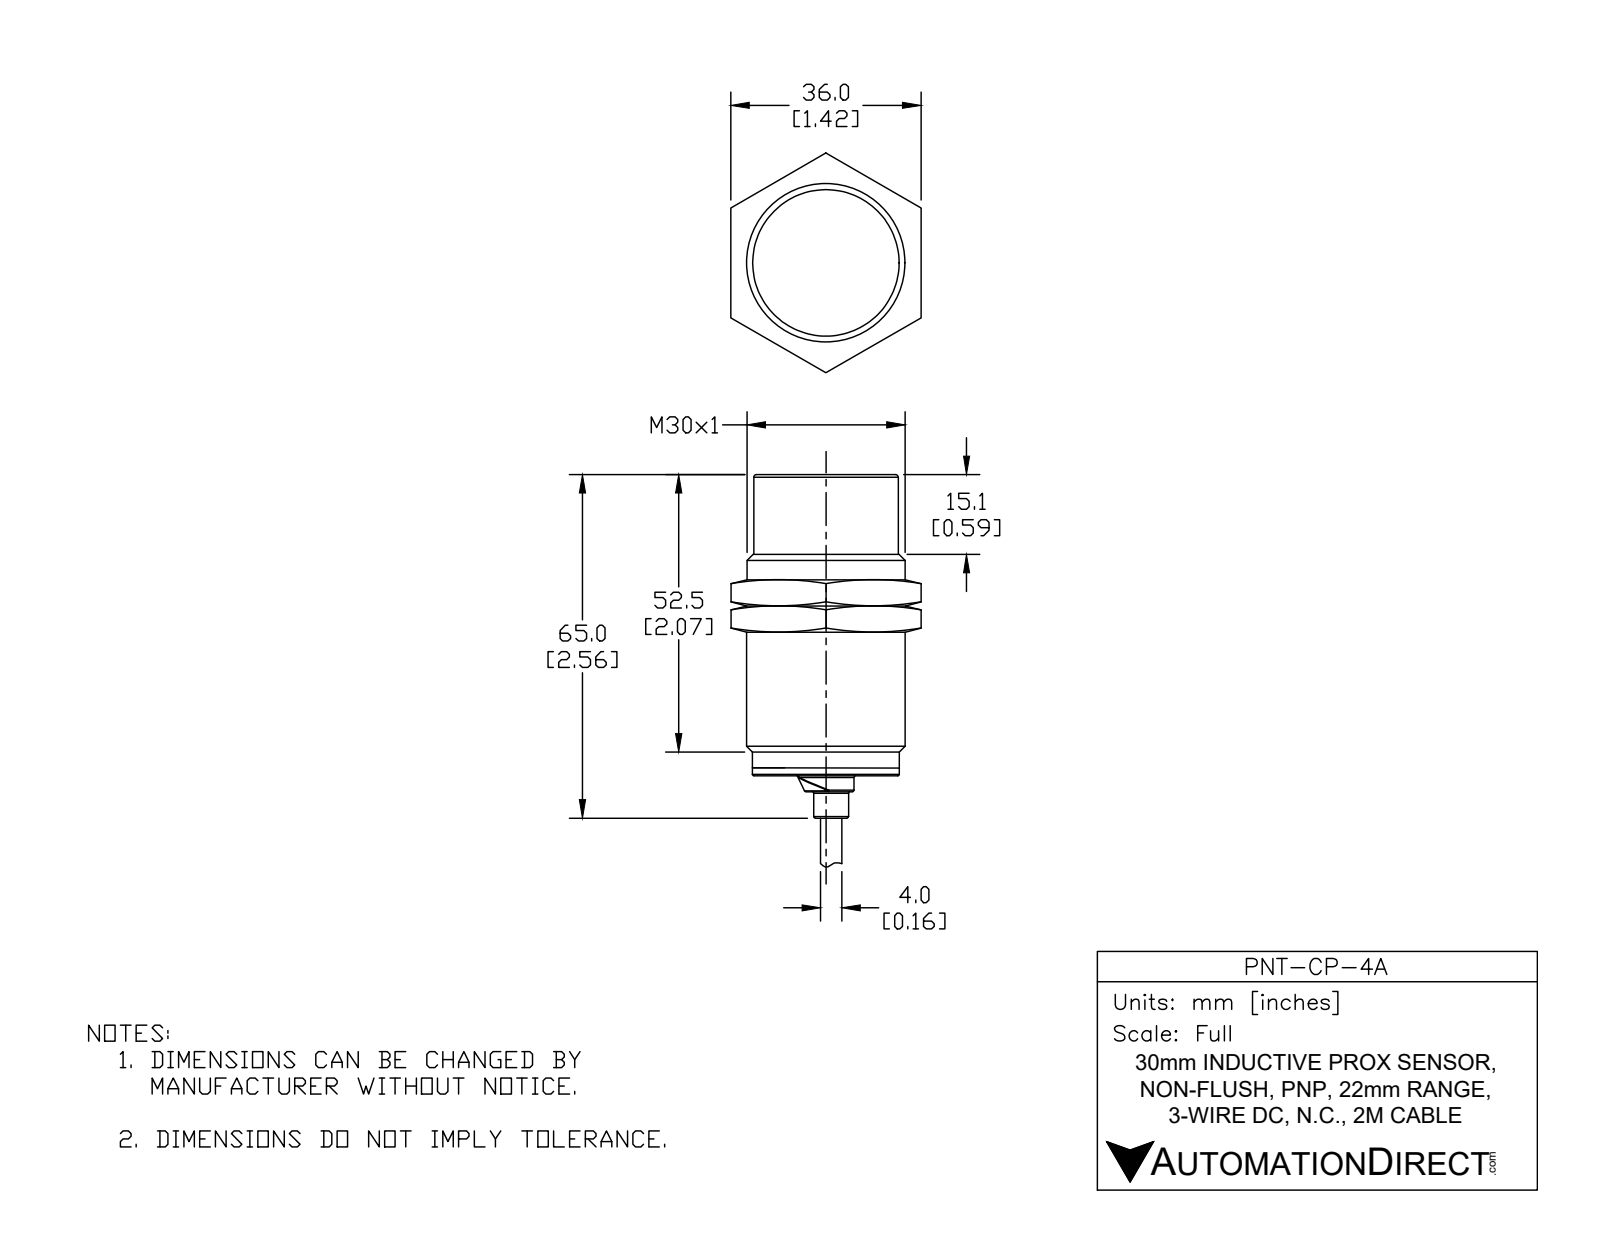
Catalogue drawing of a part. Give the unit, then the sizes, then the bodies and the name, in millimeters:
Units: millimetres
Overall size (bounding box): 115.8 × 30 × 30
Round holes (diameter × count): ⌀4.1 ×1
Round bosses / shafts (diameter × count): ⌀1.2 ×6, ⌀30 ×1, ⌀27.8 ×1, ⌀27.8 ×1, ⌀10.6 ×1, ⌀6.6 ×1, ⌀4 ×1
Partial cylindrical surfaces — rounded edges, fillets, slot ends (radius × count): R2 ×1
Main face-to-face distances: 57, 60, 3, 57.9, 65, 8, 5, 115.8, 58.8, 55.8
Volume: 40 750 mm³ · Surface area: 7 677 mm²
Bodies: 1 solid, 74 faces (14 planar, 30 cylindrical, 30 other)
Part name (STEP PRODUCT): PNT-CP-4A
STEP written by: SolidWorks 2017 (AUTOMOTIVE_DESIGN)
